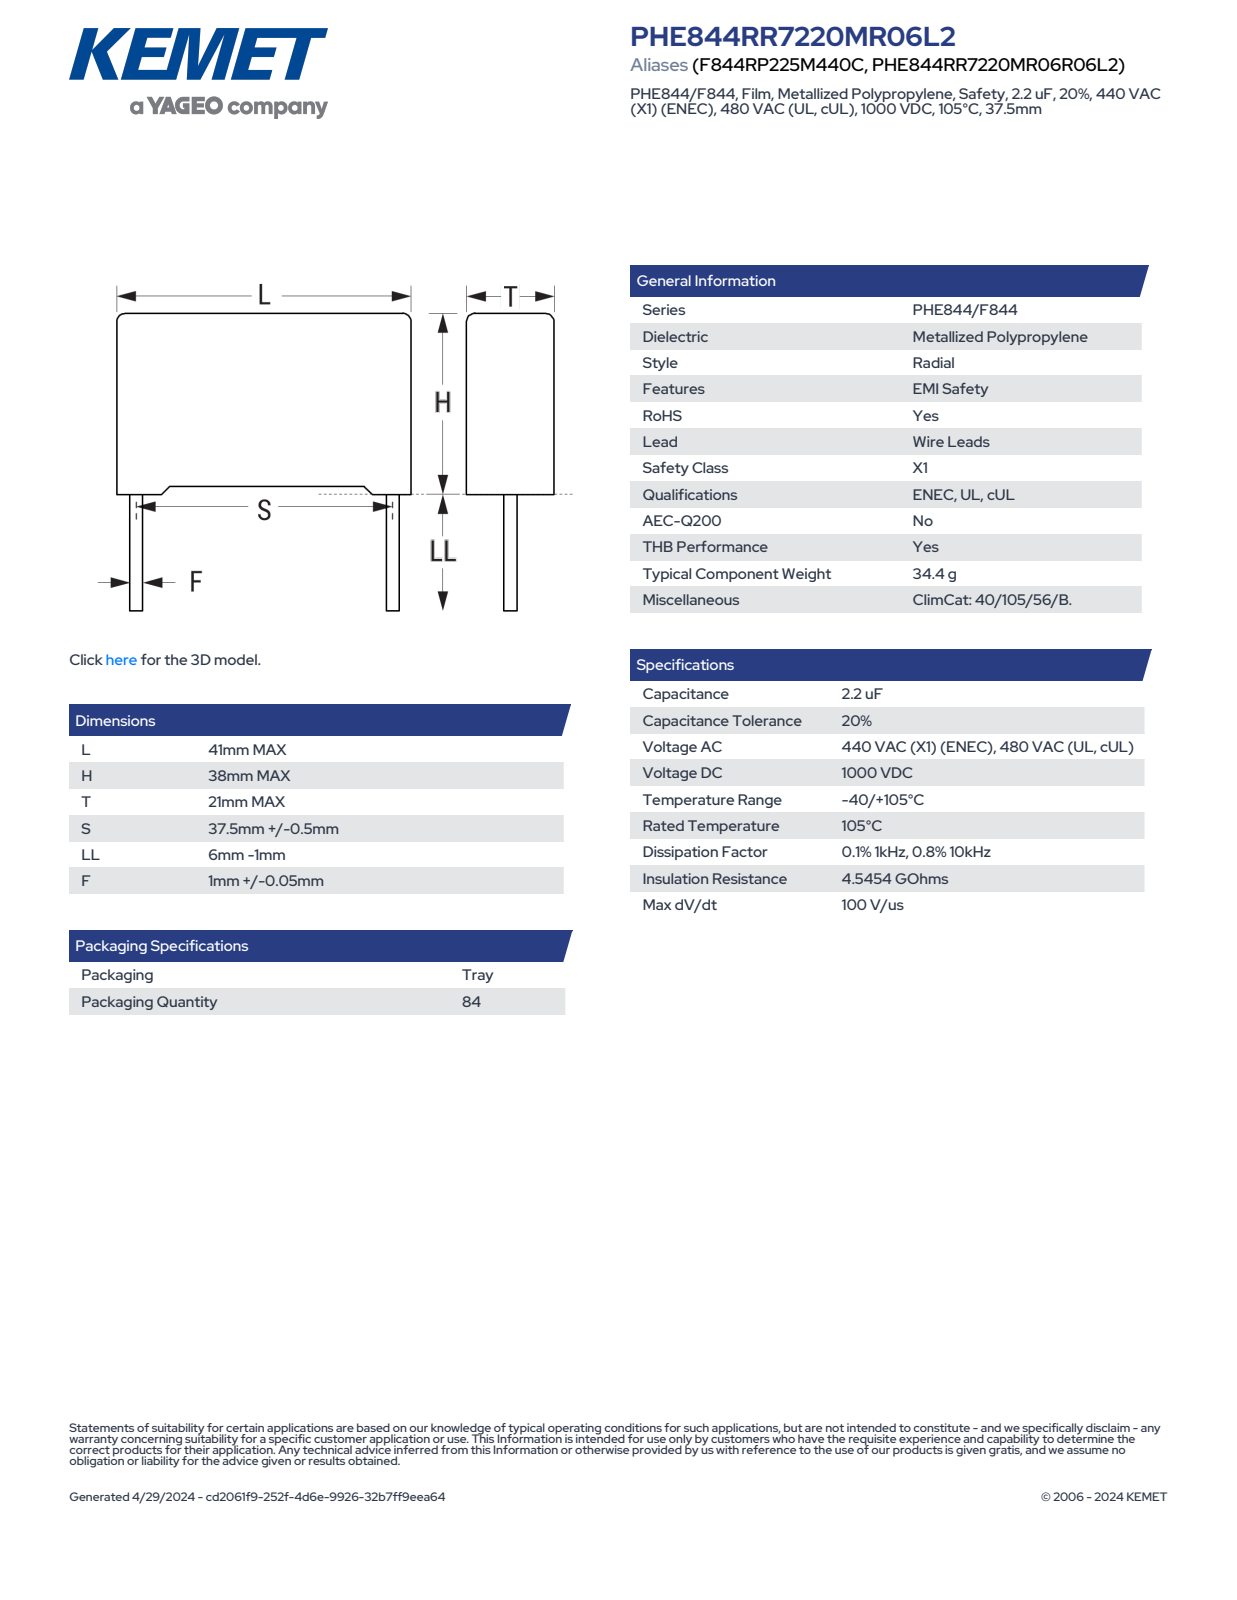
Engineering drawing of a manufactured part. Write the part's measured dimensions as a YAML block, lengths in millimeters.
part_name: "CFR_RB2_41X38X21_L41H38T21S37.5LL5F1.05"
step_written_by: "SolidWorks 2021 (AUTOMOTIVE_DESIGN)"
units: millimeters
bodies: {solids: 4, faces: 87, planar: 79, cylindrical: 8, other: 0}
overall_size: [43, 41, 21]
volume: 31743
surface_area: 6528
round_bosses_or_shafts:
  - {diameter: 1.05, count: 2}
partial_cylinders:
  - {radius: 0.5, count: 4}
face_to_face_distances: [21, 41, 36.69, 0.56, 37.25, 0.75, 1.31, 38, 1.37, 21.01]
